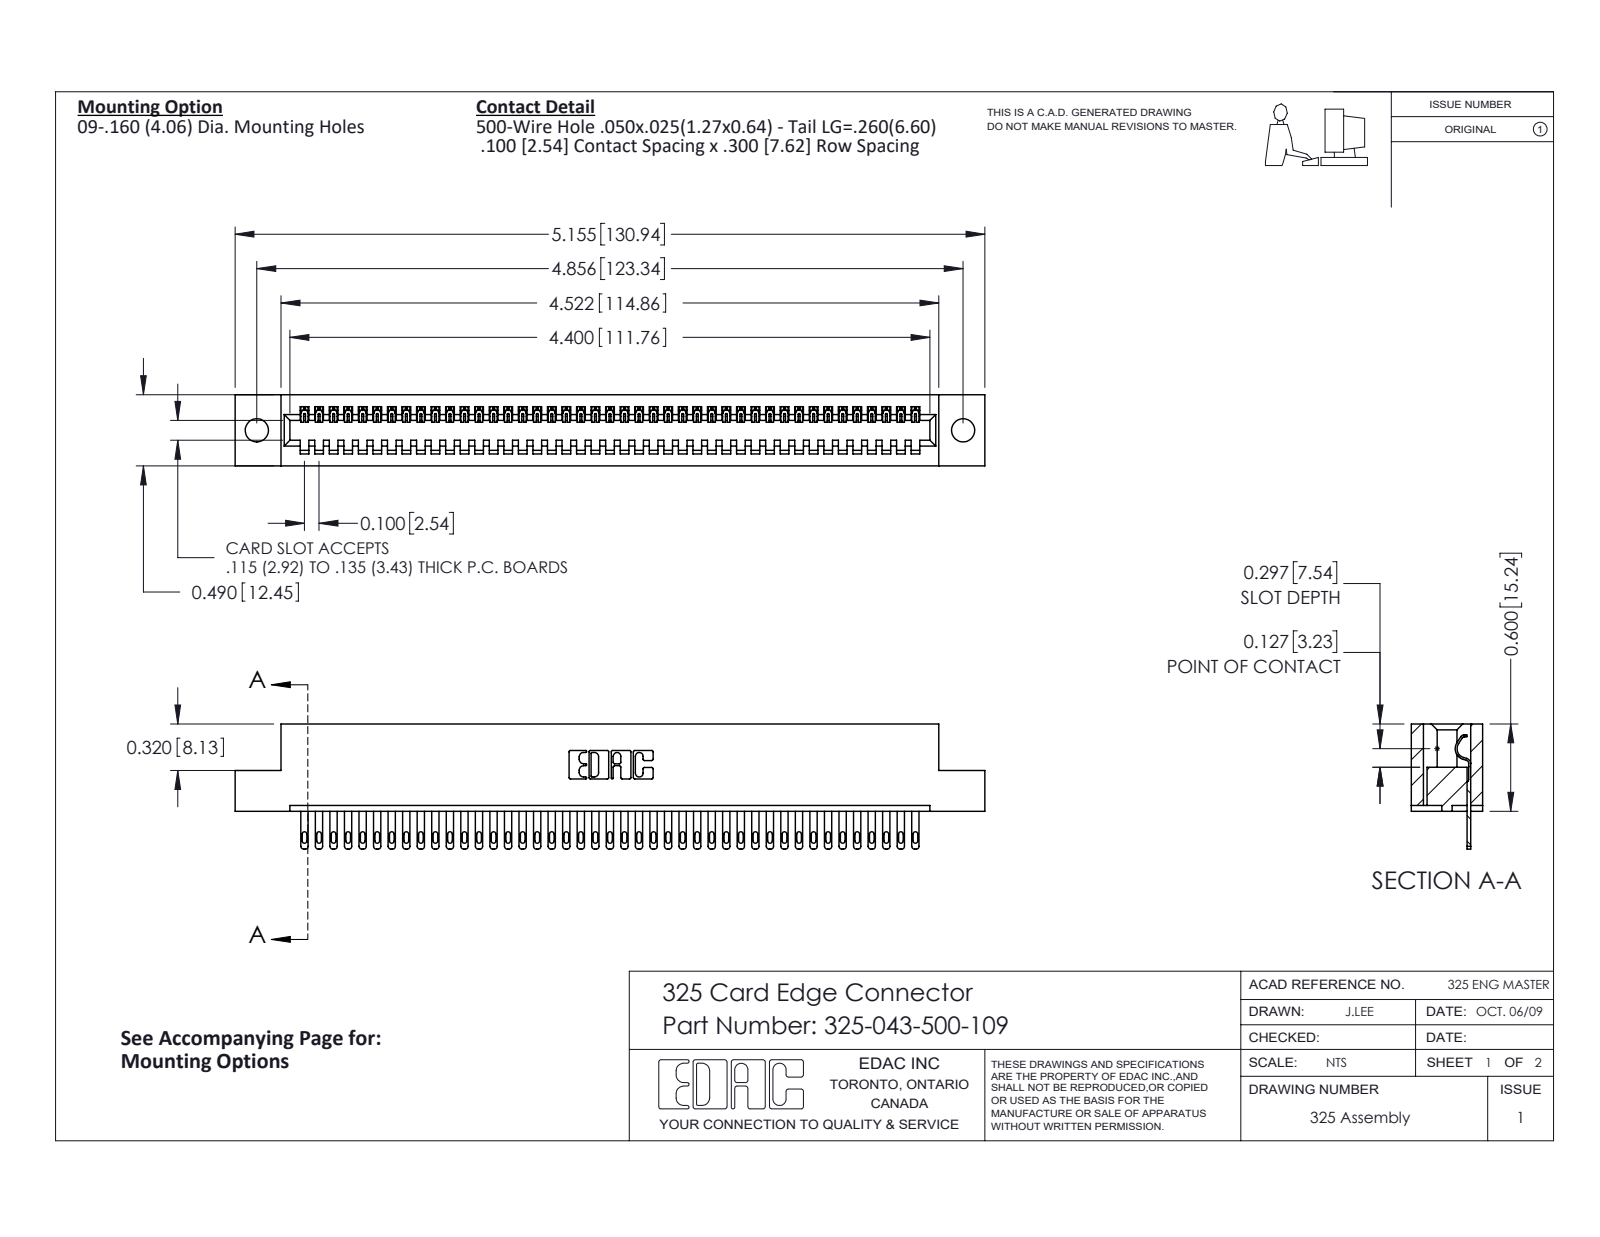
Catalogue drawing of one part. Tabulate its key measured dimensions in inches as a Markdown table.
| quantity | value |
| --- | --- |
| part name | 325-292-001_325-293-100; 325 Part_.160 TH; 325-043-500-109 |
| STEP written by | SolidWorks 2016 (CONFIG_CONTROL_DESIGN) |
| units | inches |
| bodies | 44 solids, 2436 faces (1618 planar, 818 cylindrical, 0 other) |
| overall size | 5.155 × 0.86 × 0.49 |
| volume | 1.002 in³ |
| surface area | 27.84 in² |
| round holes (diameter × count) | 0.16 × 2 |
| partial cylindrical surfaces (radius × count) | 0.006 × 86, 0.016 × 86, 0.02 × 86, 0.01 × 22, 0.007 × 6, 0.031 × 6, 0.026 × 3, 0.014 × 1 |
| main face-to-face distances | 0.083, 0.407, 0.49, 0.3, 0.107, 0.383, 0.025, 0.325, 0.56, 0.04 |
| hole center spacings | 4.856 |
